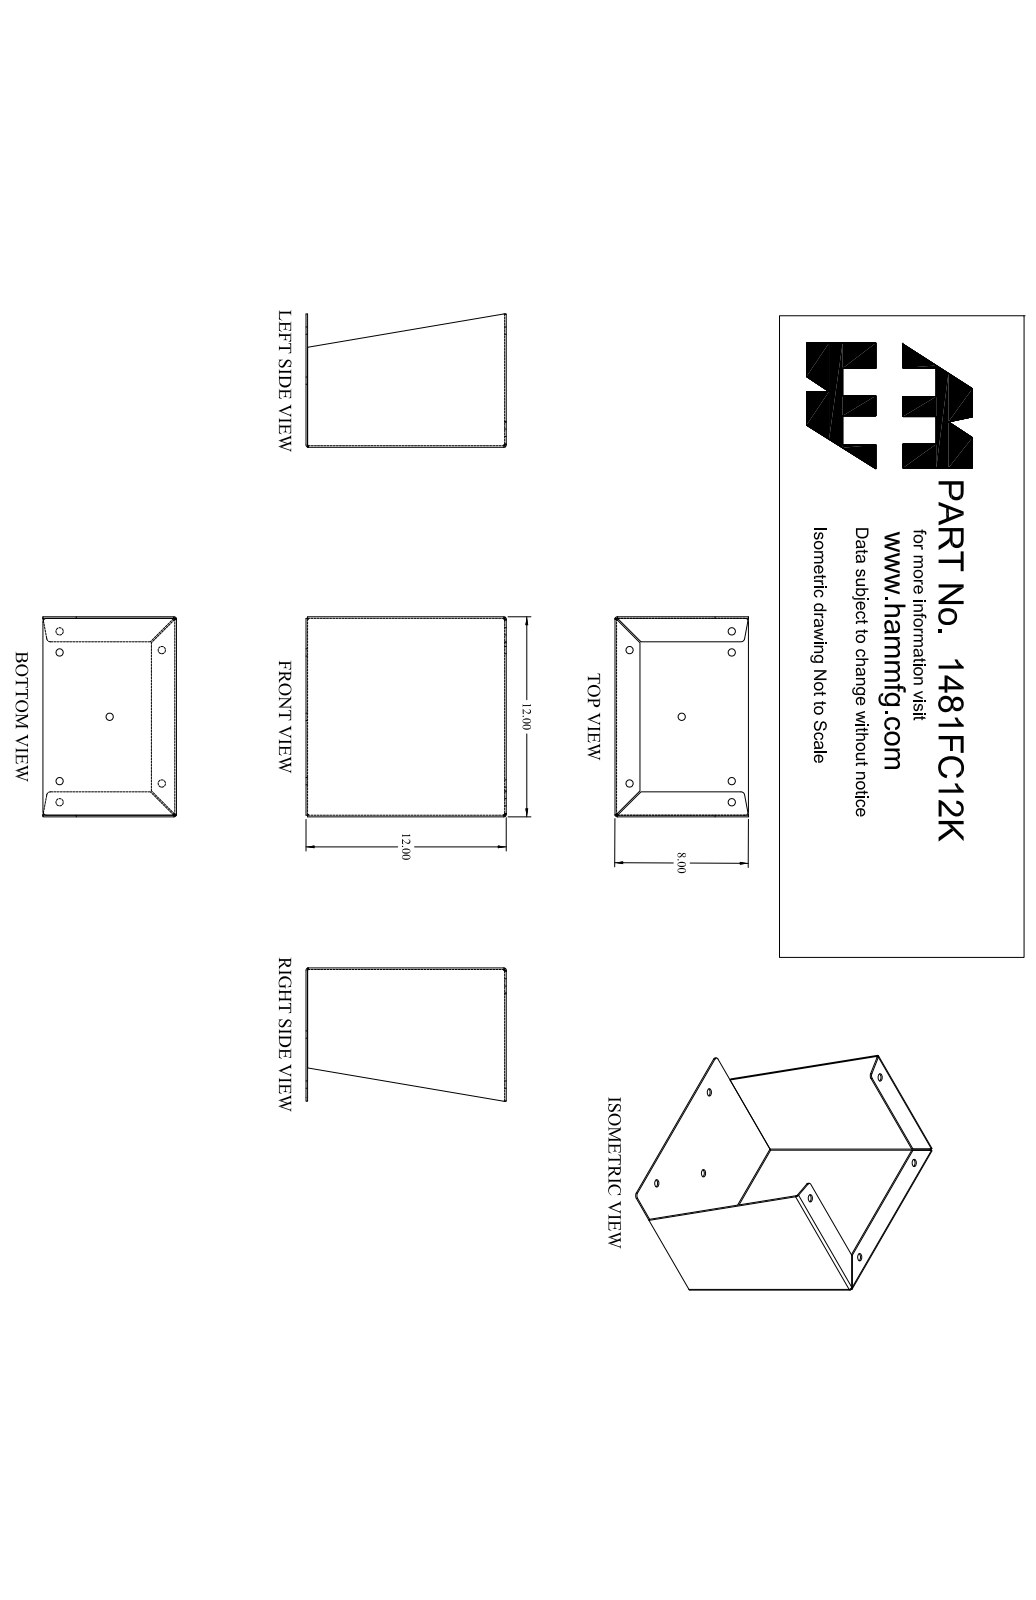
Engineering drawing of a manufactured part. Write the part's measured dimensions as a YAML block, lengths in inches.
part_name: "1481FC12K_Default"
step_written_by: "SolidWorks 2019 (CONFIG_CONTROL_DESIGN)"
units: inches
bodies: {solids: 1, faces: 78, planar: 42, cylindrical: 30, other: 6}
overall_size: [12, 12, 8]
volume: 41.08
surface_area: 875
round_holes:
  - {diameter: 0.437, count: 7}
partial_cylinders:
  - {radius: 0.048, count: 6}
  - {radius: 0.143, count: 6}
  - {radius: 0.22, count: 4}
face_to_face_distances: [0.095, 11.905, 12, 0.095, 11.81, 11.81, 11.905, 1.405, 1.5, 10.5]
hole_center_spacings: [4.888, 5.076, 6.126, 6.227, 9.964, 1.266, 1.266, 5.939]
